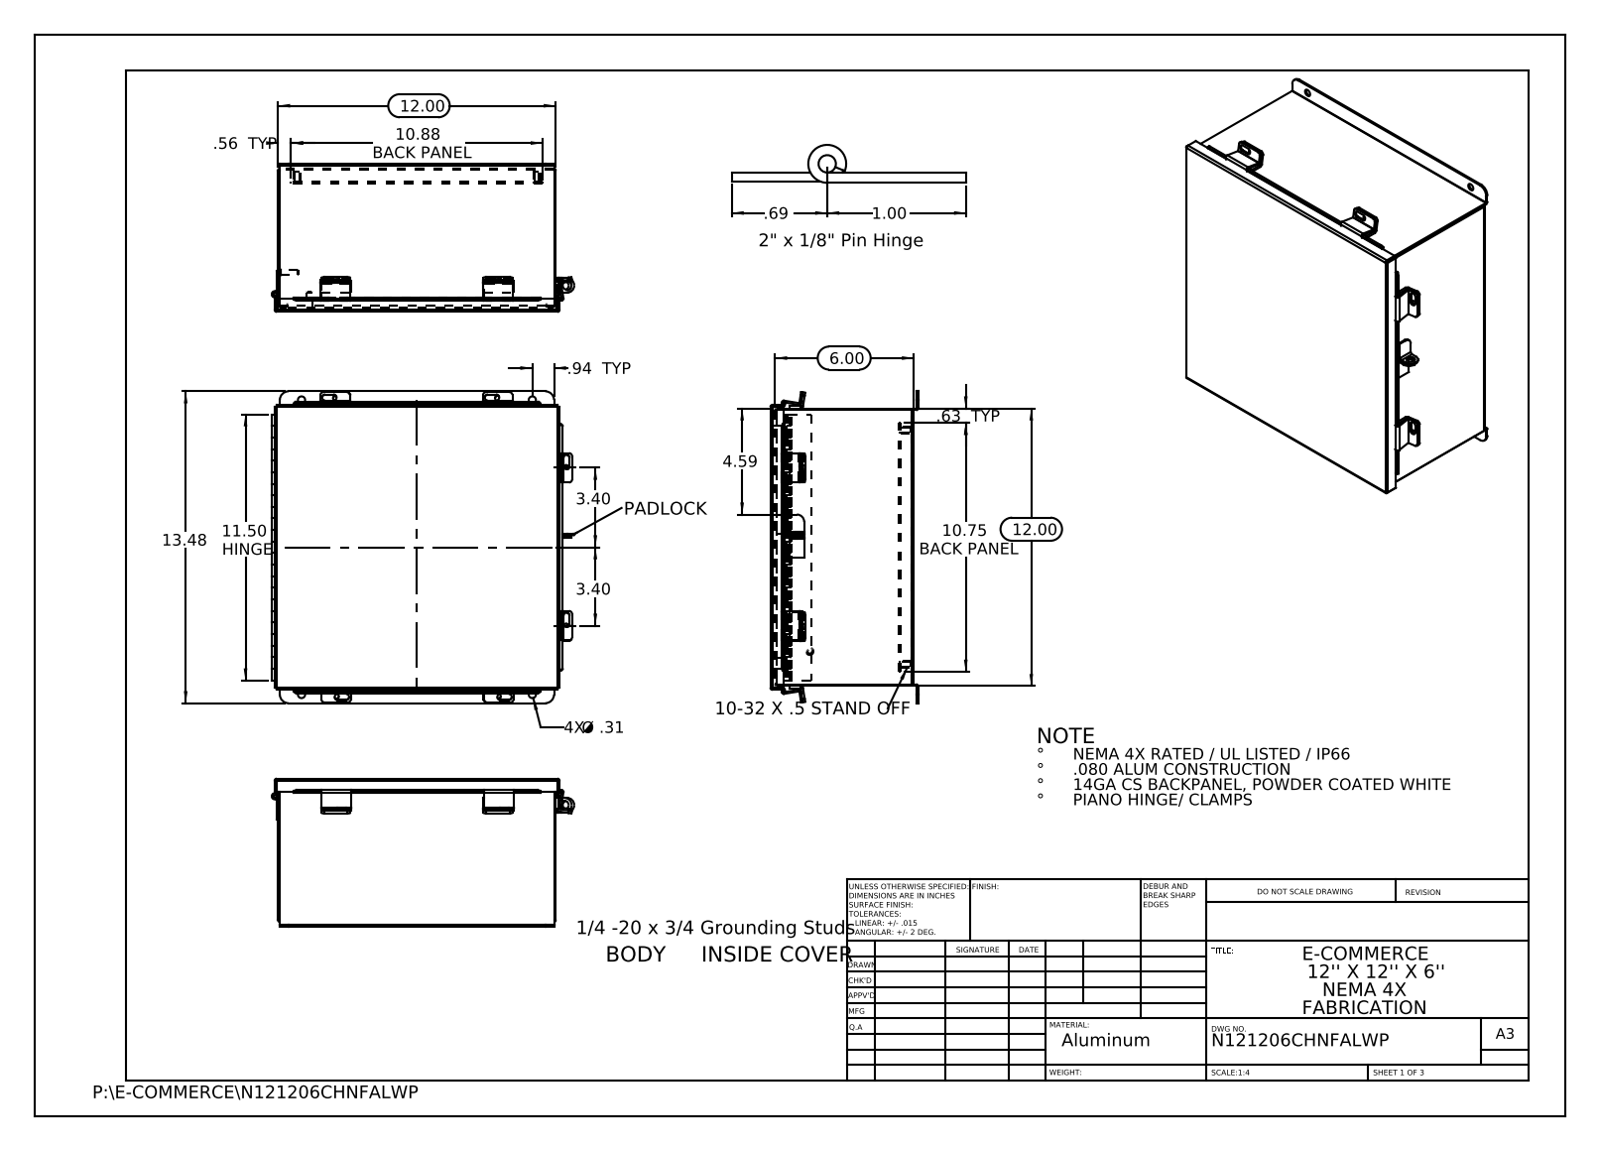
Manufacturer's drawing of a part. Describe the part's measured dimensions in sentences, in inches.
The part is named "N121206CHNFALWP JIC Cover Clamp; HW-CLH-JH-20104; N121206CHNFALWP JIC Backpanel; N121206CHNFALWP JIC_Cover_Template (+8 more)". Its 3-D file was written by "SolidWorks 2013 (CONFIG_CONTROL_DESIGN)". It is 27 solids with 794 faces: 499 planar, 275 cylindrical and 20 other. Overall it measures 13.476 by 13.072 by 6.39 inches. Its volume is 59.89 cubic inches and its surface area 1 633 square inches. Round holes: 10 of diameter 0.25, 4 of diameter 0.187, 4 of diameter 0.312, 1 of diameter 0.125, 1 of diameter 0.125, 1 of diameter 0.373, 1 of diameter 0.375. Round bosses or shafts: 4 of diameter 0.313, 2 of diameter 0.315, 2 of diameter 0.236, 1 of diameter 0.273, 1 of diameter 0.25. Partial cylindrical surfaces (rounded edges, fillets, slot ends): 21 of radius 0.125, 13 of radius 0.013, 12 of radius 0.009, 12 of radius 0.088, 12 of radius 0.133, 6 of radius 0.083, 6 of radius 0.1, 4 of radius 0.375. The main face-to-face distances are 0.075, 11.925, 6.128, 12, 11.85, 6.053, 6.203, 0.074, 0.575, 0.5. The hole center spacings are 1.315, 10.258, 11.428, 15.3, 7, 9.976, 10.126, 10.375.
